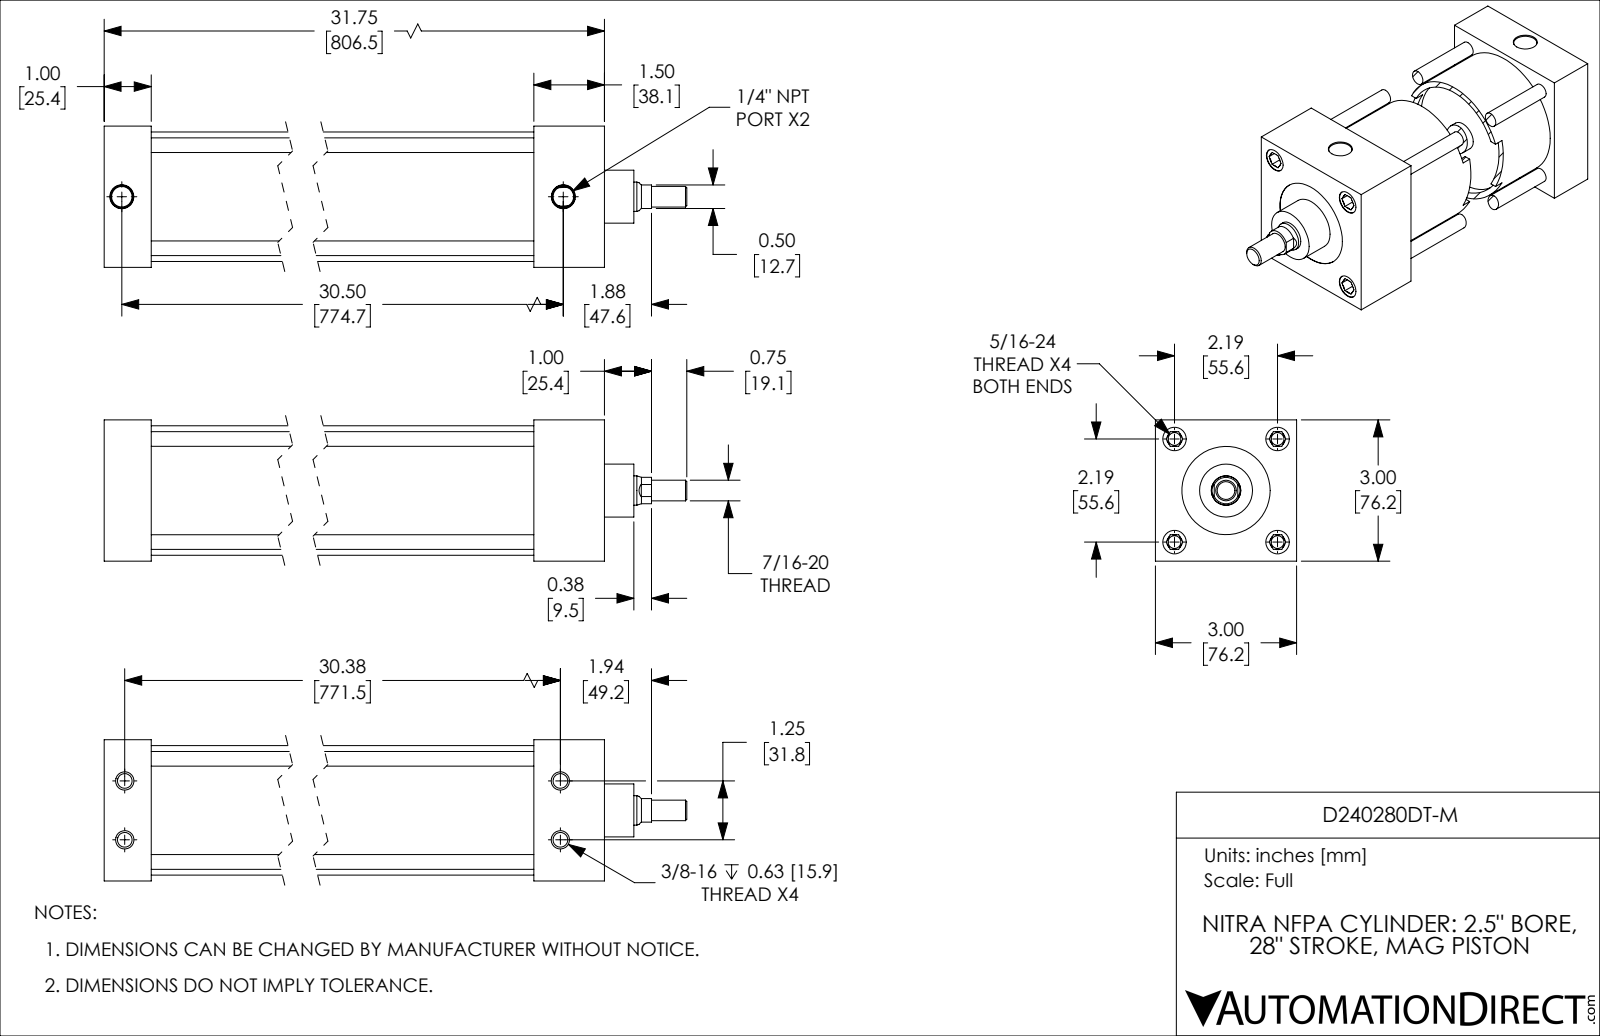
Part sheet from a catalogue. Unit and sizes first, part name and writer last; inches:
Units: inches
Overall size (bounding box): 33.5 × 3 × 3
Round holes (diameter × count): ⌀0.272 ×4, ⌀0.313 ×4, ⌀0.5 ×4, ⌀0.438 ×2, ⌀0.626 ×1, ⌀1.875 ×1, ⌀2.501 ×1
Round bosses / shafts (diameter × count): ⌀0.312 ×4, ⌀2.751 ×1, ⌀2.499 ×1, ⌀1.125 ×1, ⌀0.624 ×1, ⌀0.437 ×1
Partial cylindrical surfaces — rounded edges, fillets, slot ends (radius × count): R0.281 ×1
Main face-to-face distances: 3, 1, 30.25, 29.25, 31.75, 30.75, 1.5, 1.25, 2.25, 28
Hole centre spacings: 1.548, 2.19, 30.444, 0.628, 0.628, 1.25, 3.097, 30.375
Volume: 76.03 in³ · Surface area: 758.8 in²
Bodies: 2 solids, 200 faces (58 planar, 62 cylindrical, 80 other)
Part name (STEP PRODUCT): D240280DT-M_PISTON_KK1; D240280DT-M_BODY; D240280DT-M
STEP written by: SolidWorks 2019 (CONFIG_CONTROL_DESIGN)
